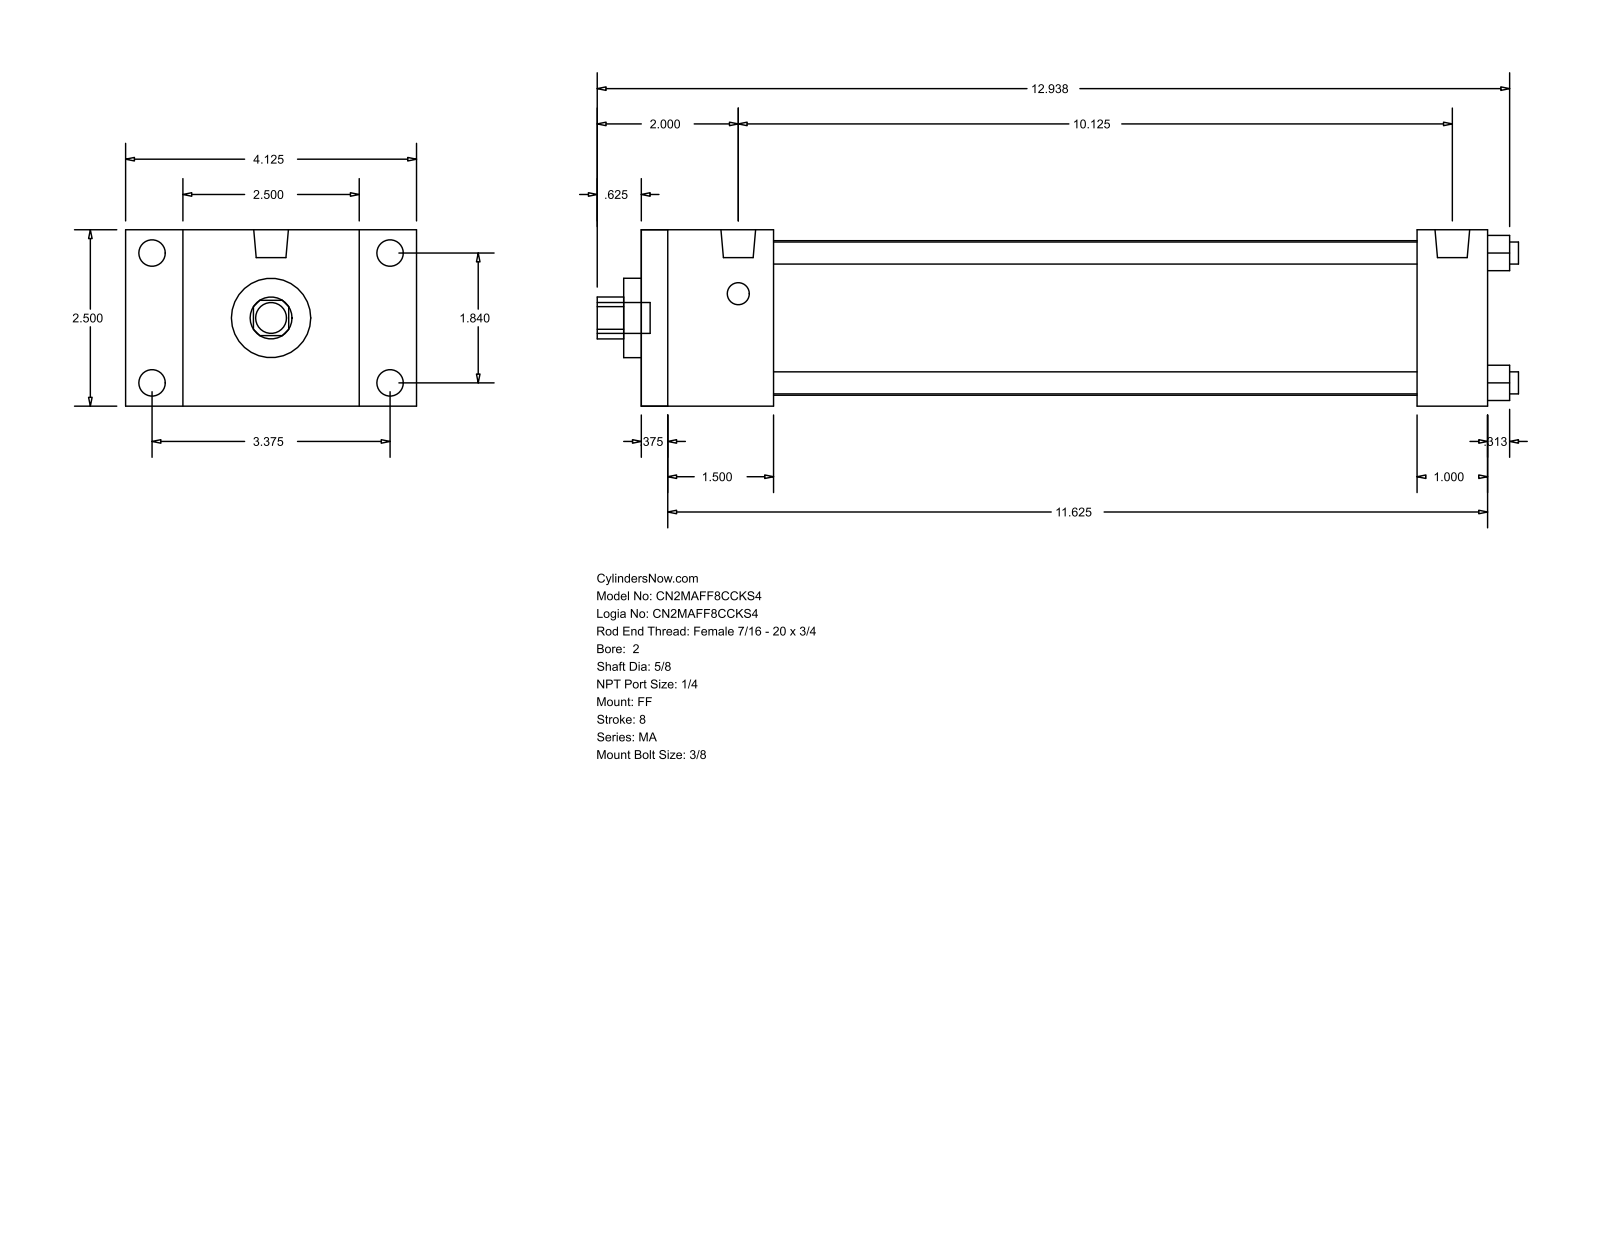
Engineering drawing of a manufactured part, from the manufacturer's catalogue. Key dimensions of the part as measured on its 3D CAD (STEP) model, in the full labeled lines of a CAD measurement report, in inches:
Part name (STEP PRODUCT): MA_FF__0200_0.625
STEP written by: GSSL Pune (CONFIG_CONTROL_DESIGN)
Units: inches
Bodies: 0 solids, 92 faces (64 planar, 28 cylindrical, 0 other)
Overall size (bounding box): 13.063 × 4.125 × 2.5
Round holes (diameter × count): ⌀0.313 ×4, ⌀0.625 ×1, ⌀1.125 ×1, ⌀2.19 ×1
Round bosses / shafts (diameter × count): ⌀0.375 ×4, ⌀0.313 ×4, ⌀0.492 ×2, ⌀0.437 ×1
Partial cylindrical surfaces — rounded edges, fillets, slot ends (radius × count): R0.297 ×1
Main face-to-face distances: 2.5, 12, 0.375, 11.625, 1.5, 1.875, 11, 10.625, 9.125, 10.125
Hole centre spacings: 1.301, 1.84, 2.602
